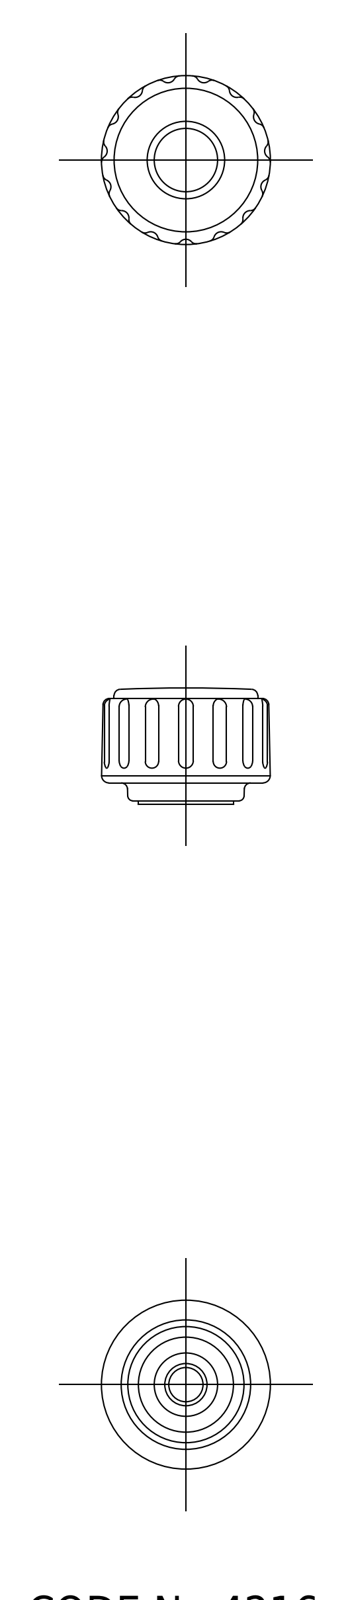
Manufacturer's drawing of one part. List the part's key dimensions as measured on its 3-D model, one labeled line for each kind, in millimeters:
Part name (STEP PRODUCT): screw; knob; KDF_16_M4_22697_36
STEP written by: CADfix (AUTOMOTIVE_DESIGN)
Units: millimetres
Bodies: 2 solids, 65 faces (0 planar, 0 cylindrical, 65 other)
Overall size (bounding box): 15.97 × 15.97 × 10.96
Volume: 1 756 mm³ · Surface area: 1 161 mm²
